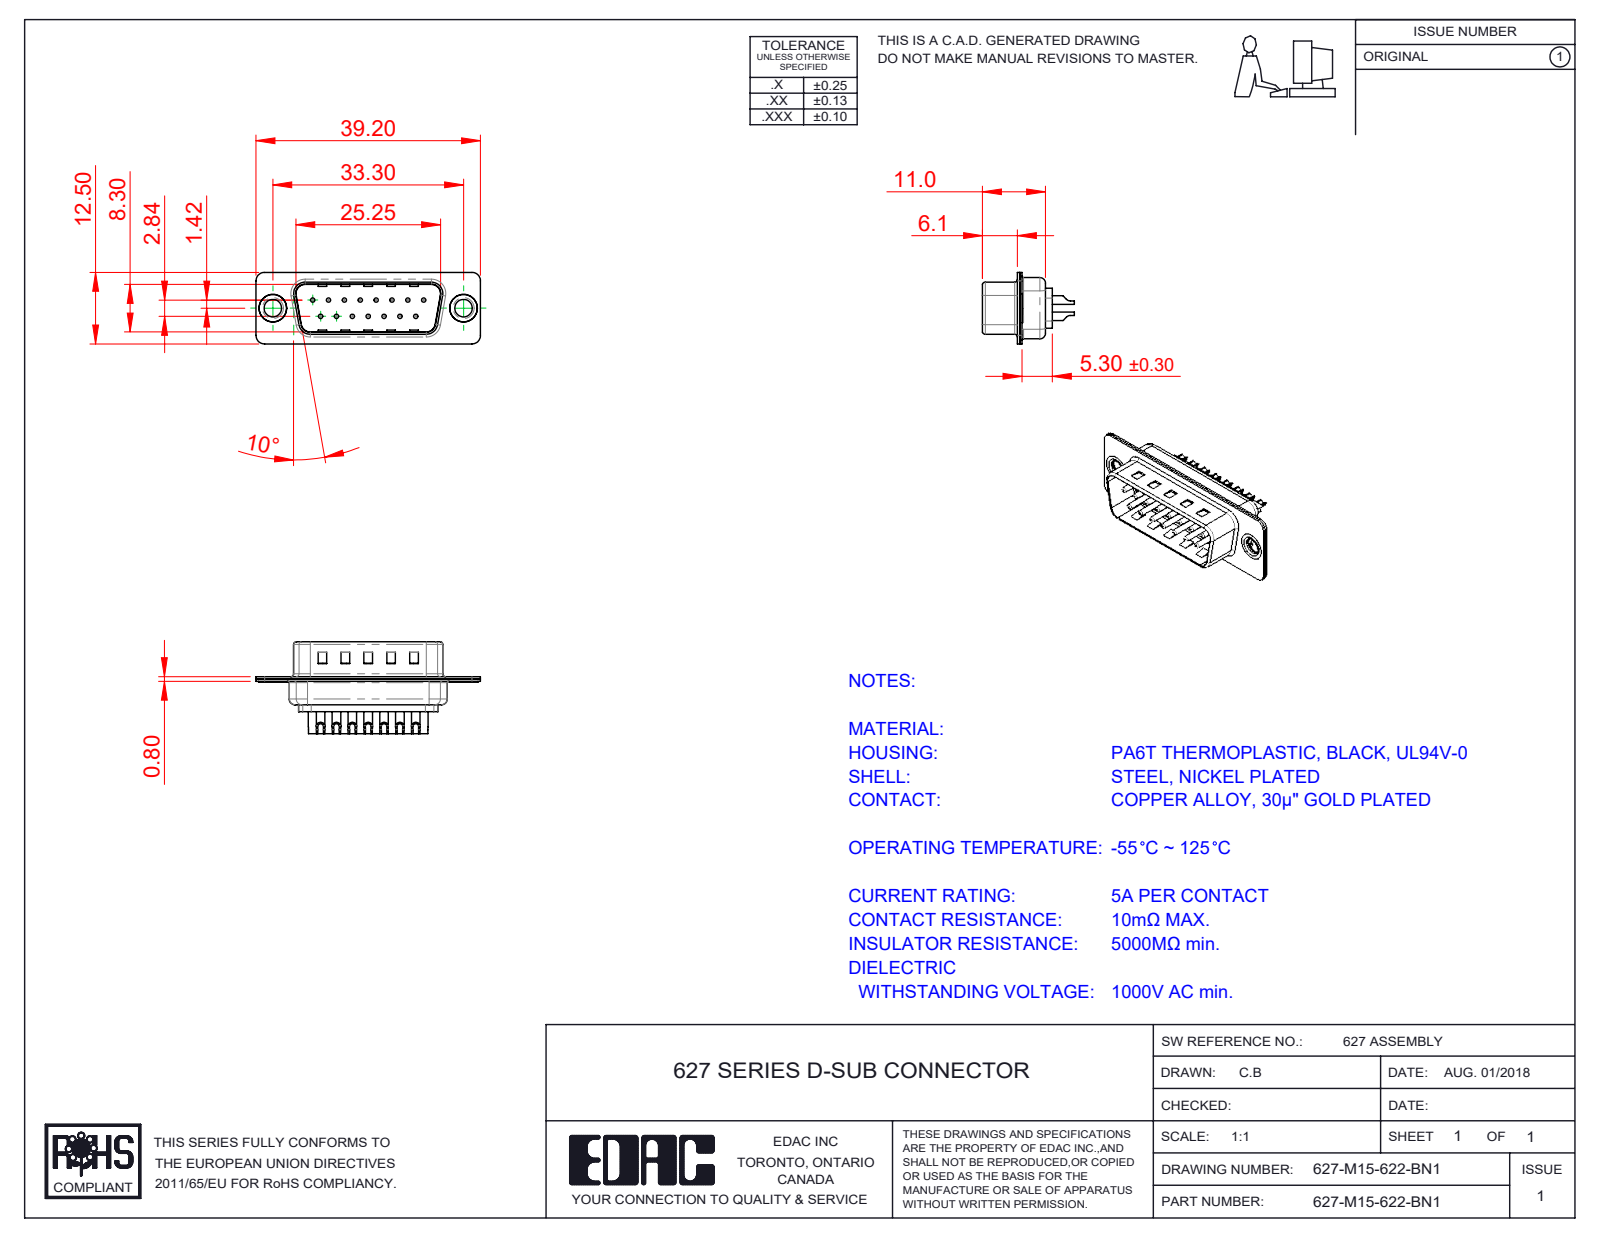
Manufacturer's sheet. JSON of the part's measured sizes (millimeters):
{"part_name": "627M Thru Hole Rivet; 627M Contact Row 2_22; 627-M15-622-BN1; 627M Contact Row 1_22 (+3 more)", "step_written_by": "SolidWorks 2020 (CONFIG_CONTROL_DESIGN)", "units": "millimeters", "bodies": {"solids": 20, "faces": 869, "planar": 274, "cylindrical": 357, "other": 238}, "overall_size": [39.2, 16.05, 12.5], "volume_mm3": 1800, "surface_area_mm2": 4804, "round_holes": [[0.75, 15], [1, 15], [1.6, 15], [2, 15], [3.05, 2], [4, 2], [4.8, 2]], "round_bosses_or_shafts": [[1.5, 15], [5, 2], [4.9, 2], [3.55, 2]], "partial_cylinders_radius": [[1.5, 16], [2, 12], [0.5, 8], [1.6, 8], [1, 6], [0.25, 4], [0.6, 4], [0.65, 4]], "face_to_face_distances": [0.4, 0.8, 9.5, 9.1, 8.7, 9.9, 1.2, 0.75, 0.35, 6.1], "hole_center_spacings": [3.16, 2.77, 5.54, 8.31, 11.08, 5.03, 5.04, 7.48]}
